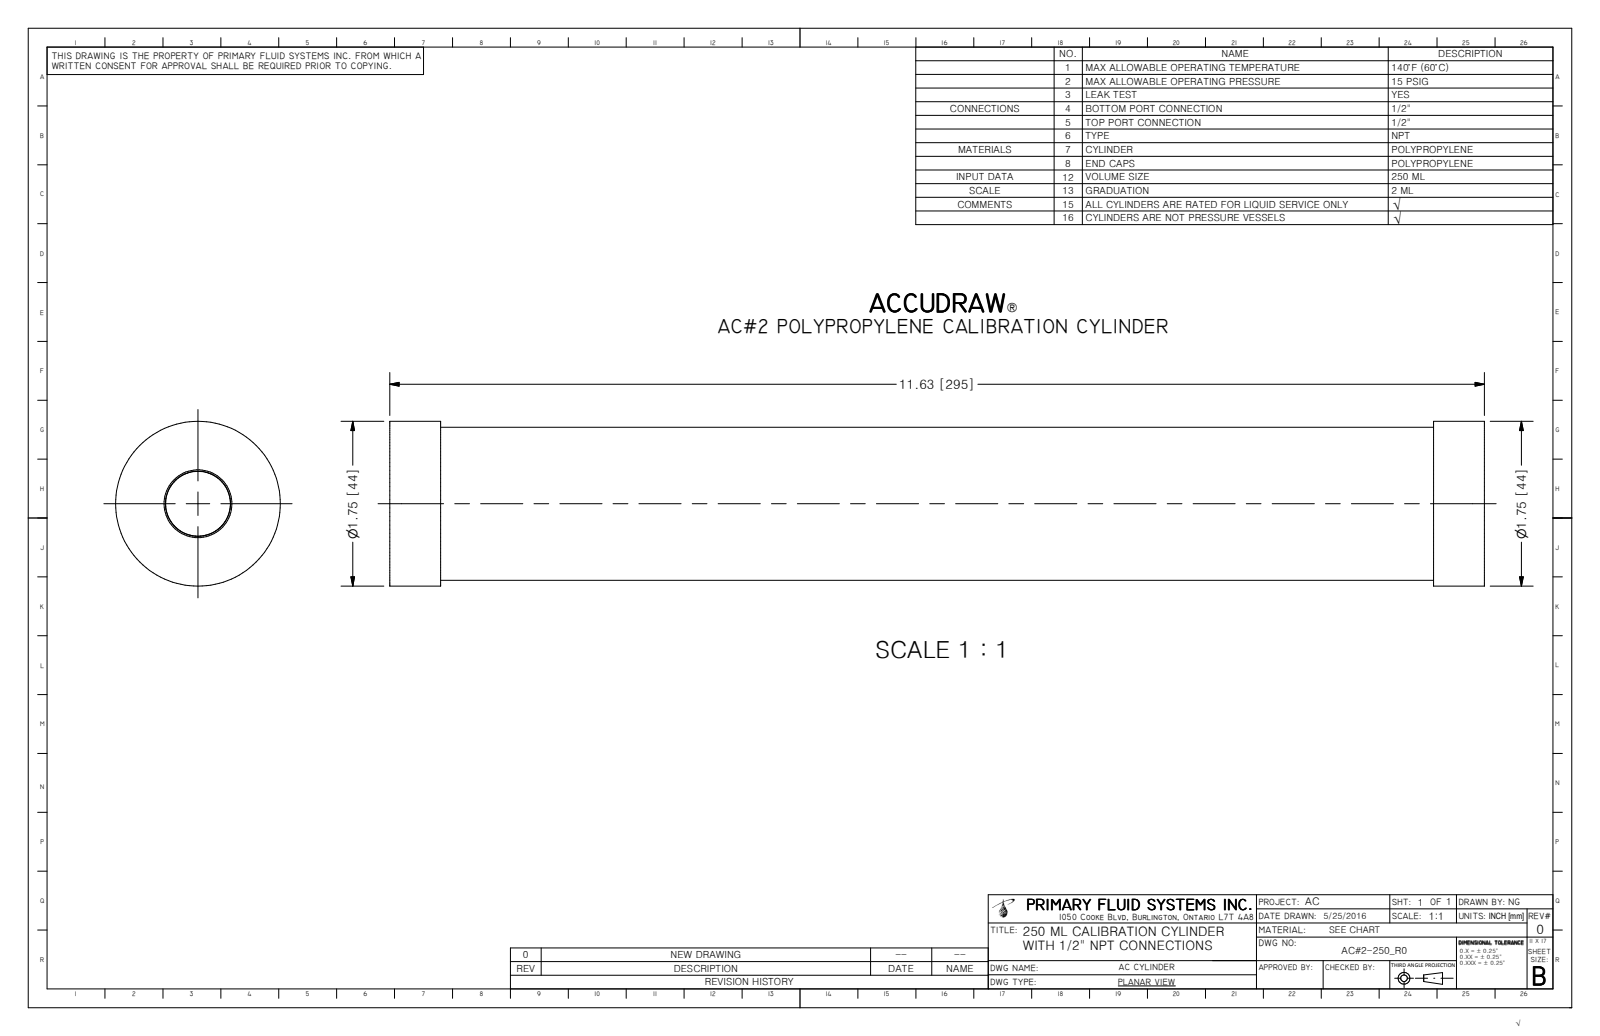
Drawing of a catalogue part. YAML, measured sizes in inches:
part_name: "AC#2-250_R0; AC-2B-250; AC-250-TUBE; AC-2T-250"
step_written_by: "Autodesk Inventor 2009 (AUTOMOTIVE_DESIGN)"
units: inches
bodies: {solids: 3, faces: 20, planar: 8, cylindrical: 6, other: 6}
overall_size: [11.63, 1.75, 1.75]
volume: 5.816
surface_area: 123.5
round_holes:
  - {diameter: 1.505, count: 1}
round_bosses_or_shafts:
  - {diameter: 1.75, count: 1}
  - {diameter: 1.625, count: 1}
  - {diameter: 1.49, count: 1}
  - {diameter: 1.385, count: 1}
face_to_face_distances: [0.75, 10.88, 11.63, 0.54, 10.34, 11.09, 0.21, 10.13, 11.09, 10.55]
